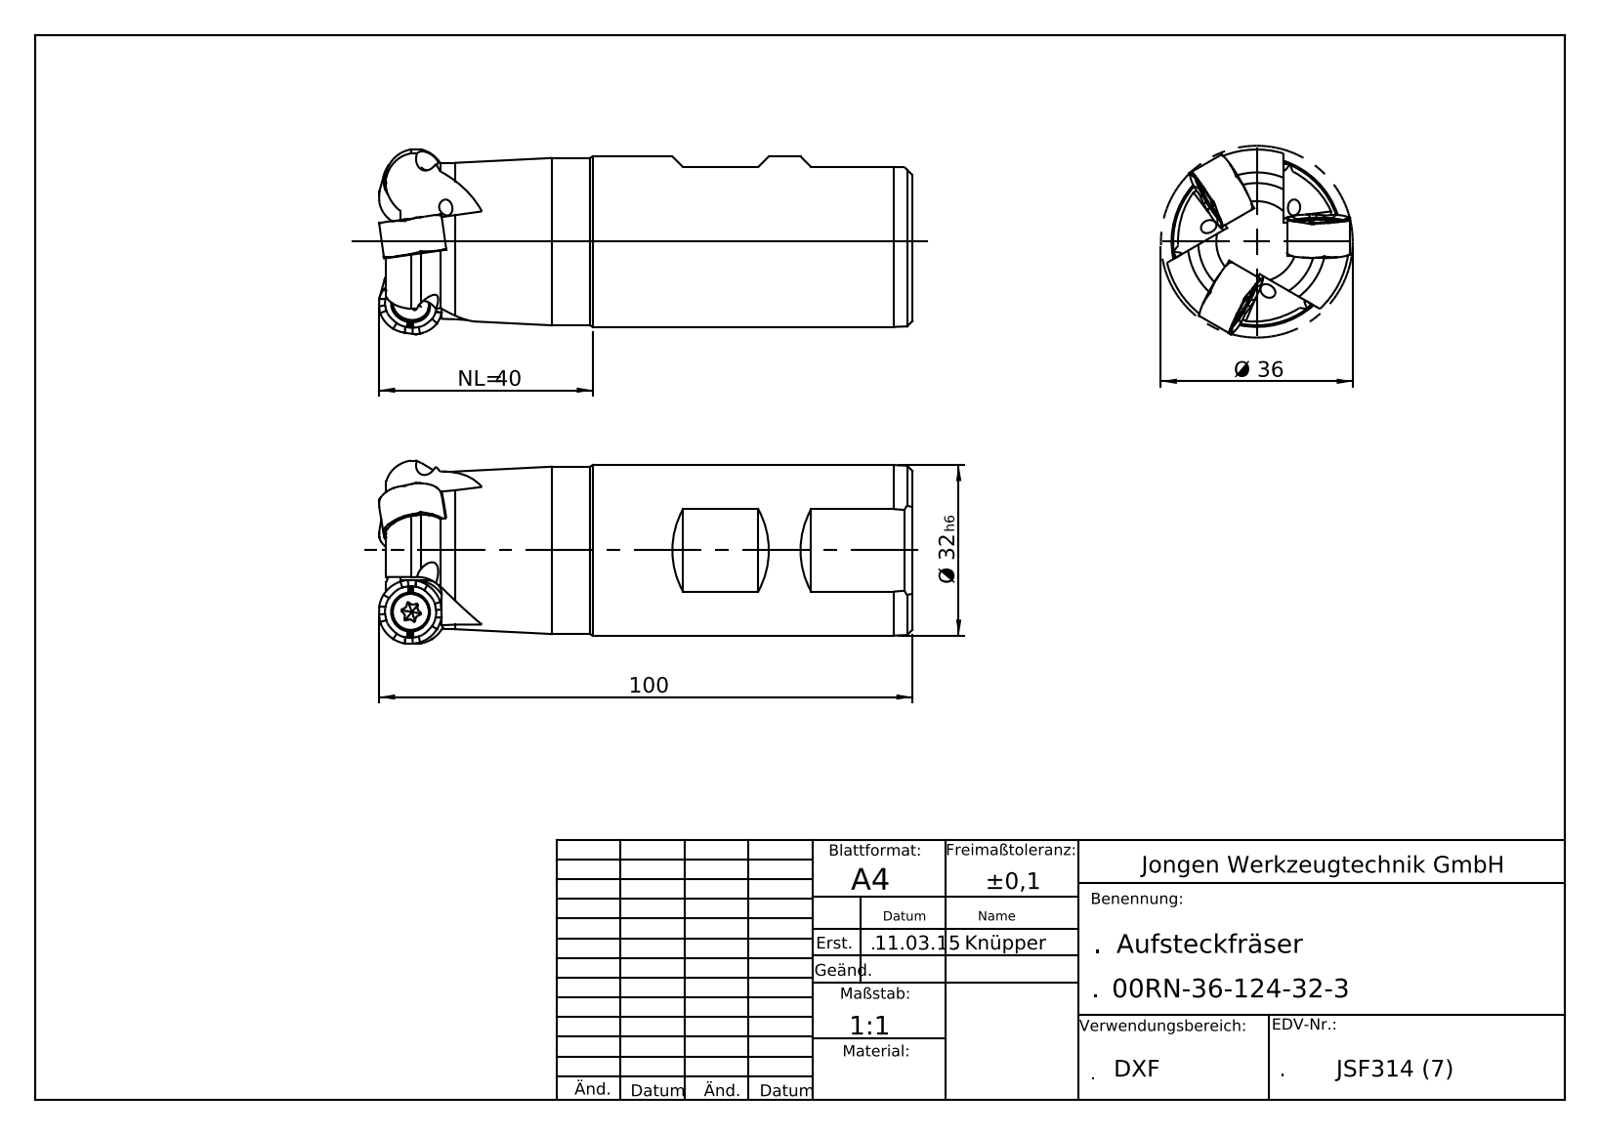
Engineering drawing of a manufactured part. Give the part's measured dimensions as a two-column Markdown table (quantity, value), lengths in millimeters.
| quantity | value |
| --- | --- |
| part name | 00RN_36_124_32_3 |
| STEP written by | SolidWorks 2016 (AUTOMOTIVE_DESIGN) |
| units | millimeters |
| bodies | 1 solid, 93 faces (41 planar, 30 cylindrical, 22 other) |
| overall size | 99.97 × 35.93 × 35.93 |
| volume | 74 460 mm³ |
| surface area | 14 534 mm² |
| round holes (diameter × count) | 3 × 3, 6.5 × 1 |
| round bosses / shafts (diameter × count) | 32 × 1, 31.4 × 1 |
| partial cylindrical surfaces (radius × count) | 2.15 × 3, 2.5 × 3, 4.5 × 3, 6 × 3, 14.8 × 1 |
| main face-to-face distances | 96.05, 6.2, 29.37, 12.37, 17, 0.6, 5.6, 0.67 |
